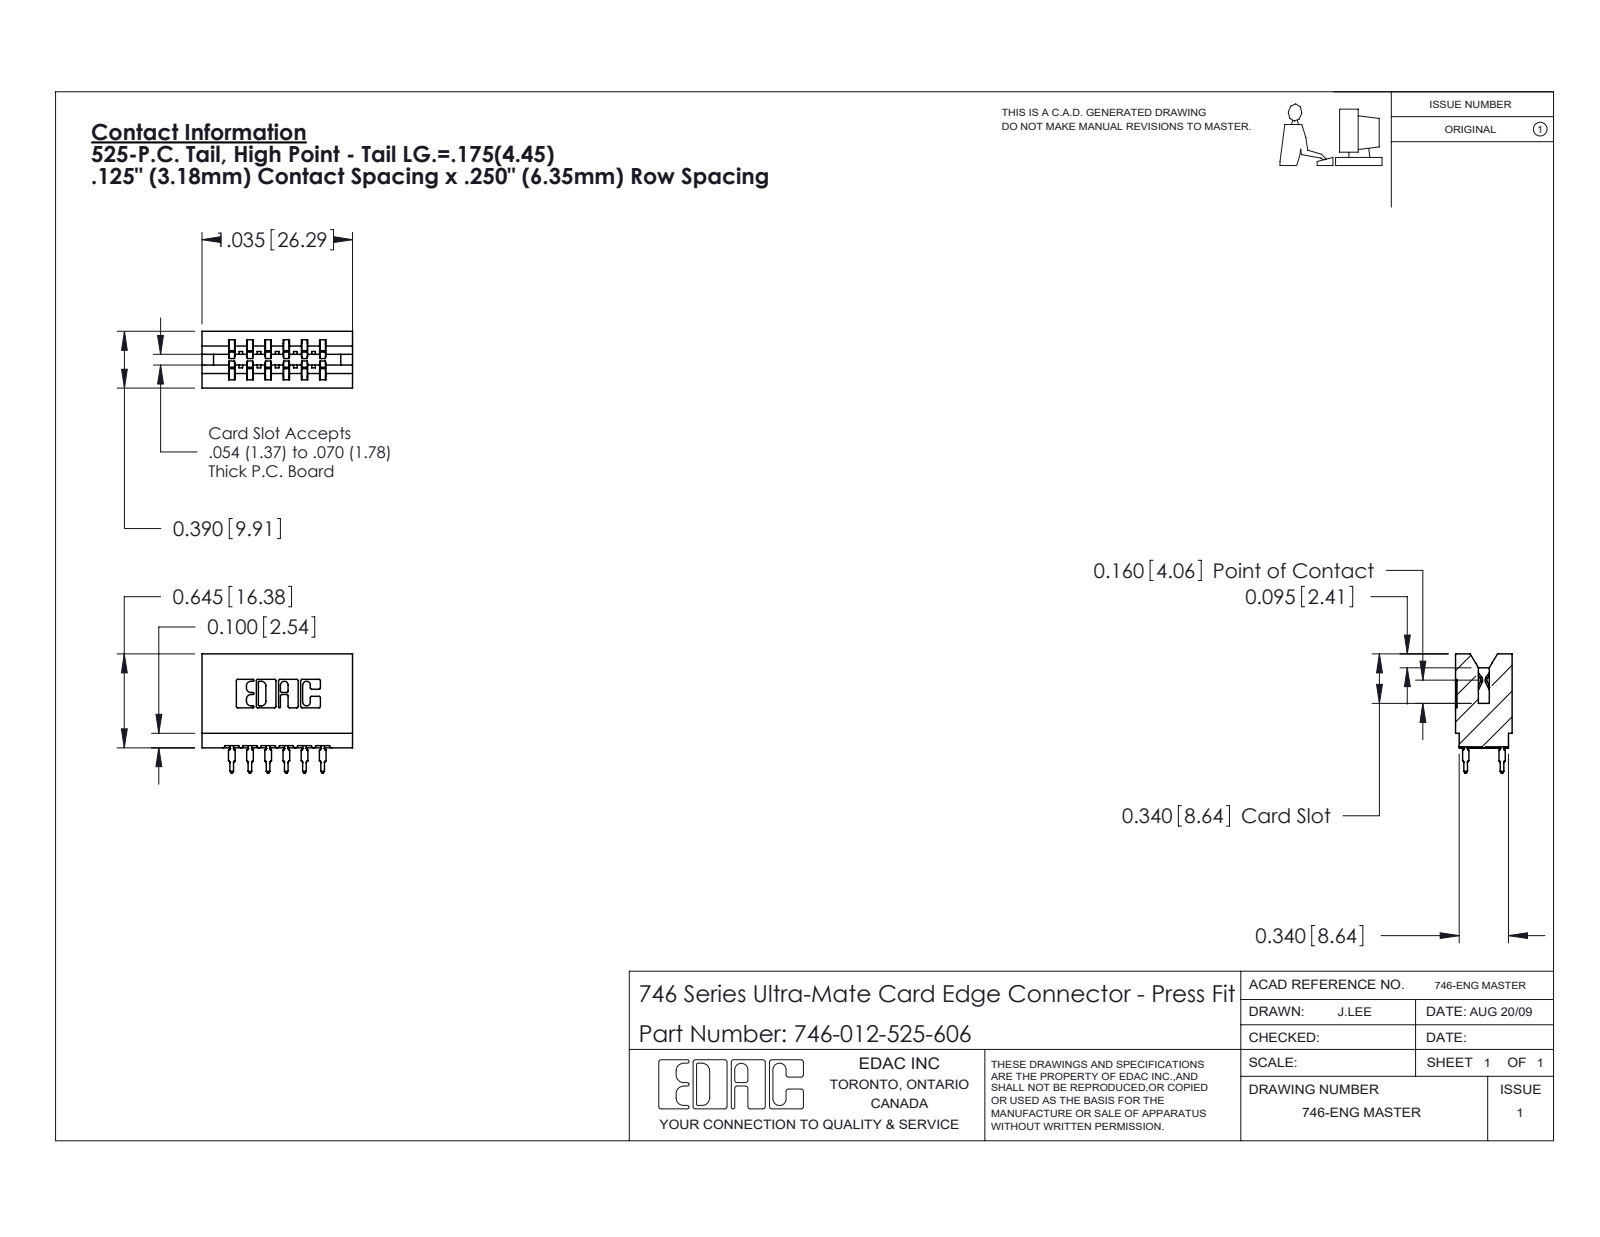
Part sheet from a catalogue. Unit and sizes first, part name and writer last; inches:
Units: inches
Overall size (bounding box): 1.035 × 0.819 × 0.39
Partial cylindrical surfaces — rounded edges, fillets, slot ends (radius × count): R0.021 ×24, R0.01 ×22, R0.005 ×8, R0.011 ×8, R0.015 ×7, R0.007 ×6, R0.031 ×6, R0.026 ×3
Main face-to-face distances: 0.25, 0.125, 0.042, 0.057, 0.333, 0.125, 0.39, 0.292, 0.375, 0.5
Volume: 0.195 in³ · Surface area: 6.221 in²
Bodies: 13 solids, 1172 faces (608 planar, 252 cylindrical, 312 other)
Part name (STEP PRODUCT): 746 Part_.340 Slot Depth - 06; 746-292-001_525; 746-012-525-606
STEP written by: SolidWorks 2020 (CONFIG_CONTROL_DESIGN)
